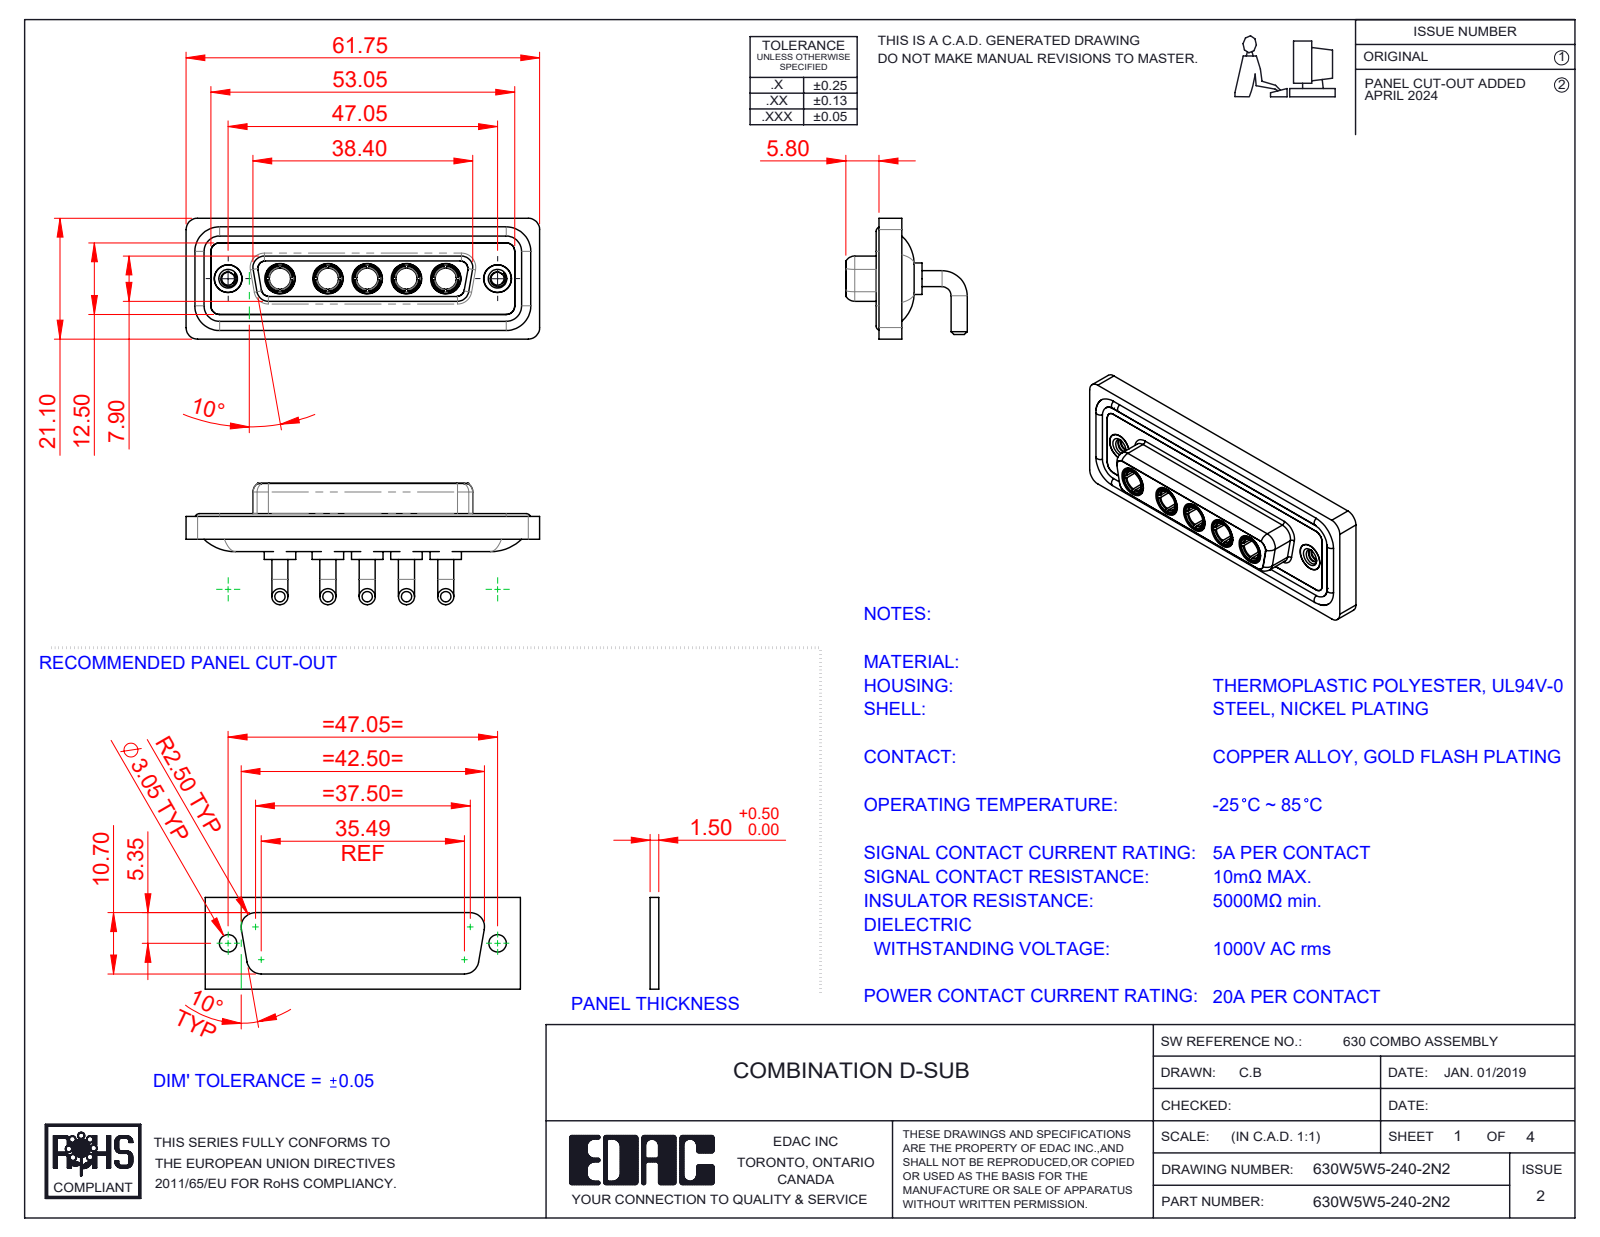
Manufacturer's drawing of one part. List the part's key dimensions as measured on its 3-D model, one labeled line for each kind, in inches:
Part name (STEP PRODUCT): 630Combo Threaded Rivet_2; 630Combo Shell Rear_25 Contacts; 630Combo Housing_5W5; Power Socket_20A RA (+3 more)
STEP written by: SolidWorks 2023 (CONFIG_CONTROL_DESIGN)
Units: inches
Bodies: 17 solids, 776 faces (250 planar, 313 cylindrical, 213 other)
Overall size (bounding box): 2.431 × 0.835 × 0.831
Volume: 0.515 in³ · Surface area: 21.41 in²
Round holes (diameter × count): ⌀0.191 ×7, ⌀0.146 ×5, ⌀0.209 ×5, ⌀0.089 ×2, ⌀0.157 ×2, ⌀0.159 ×2, ⌀0.197 ×2
Round bosses / shafts (diameter × count): ⌀0.11 ×10, ⌀0.217 ×5, ⌀0.205 ×5, ⌀0.195 ×5, ⌀0.187 ×5, ⌀0.148 ×5, ⌀0.063 ×4, ⌀0.195 ×2
Partial cylindrical surfaces — rounded edges, fillets, slot ends (radius × count): R0.059 ×18, R0.079 ×18, R0.053 ×8, R0.063 ×8, R0.083 ×5, R0.01 ×4, R0.02 ×4, R0.024 ×4
Main face-to-face distances: 0.016, 0.071, 0.161, 0.043, 0.059, 0.098, 0.122, 0.146, 0.063, 0.114
Hole centre spacings: 0.27, 0.356, 1.496, 0.27, 0.33, 0.54, 0.541, 0.6
